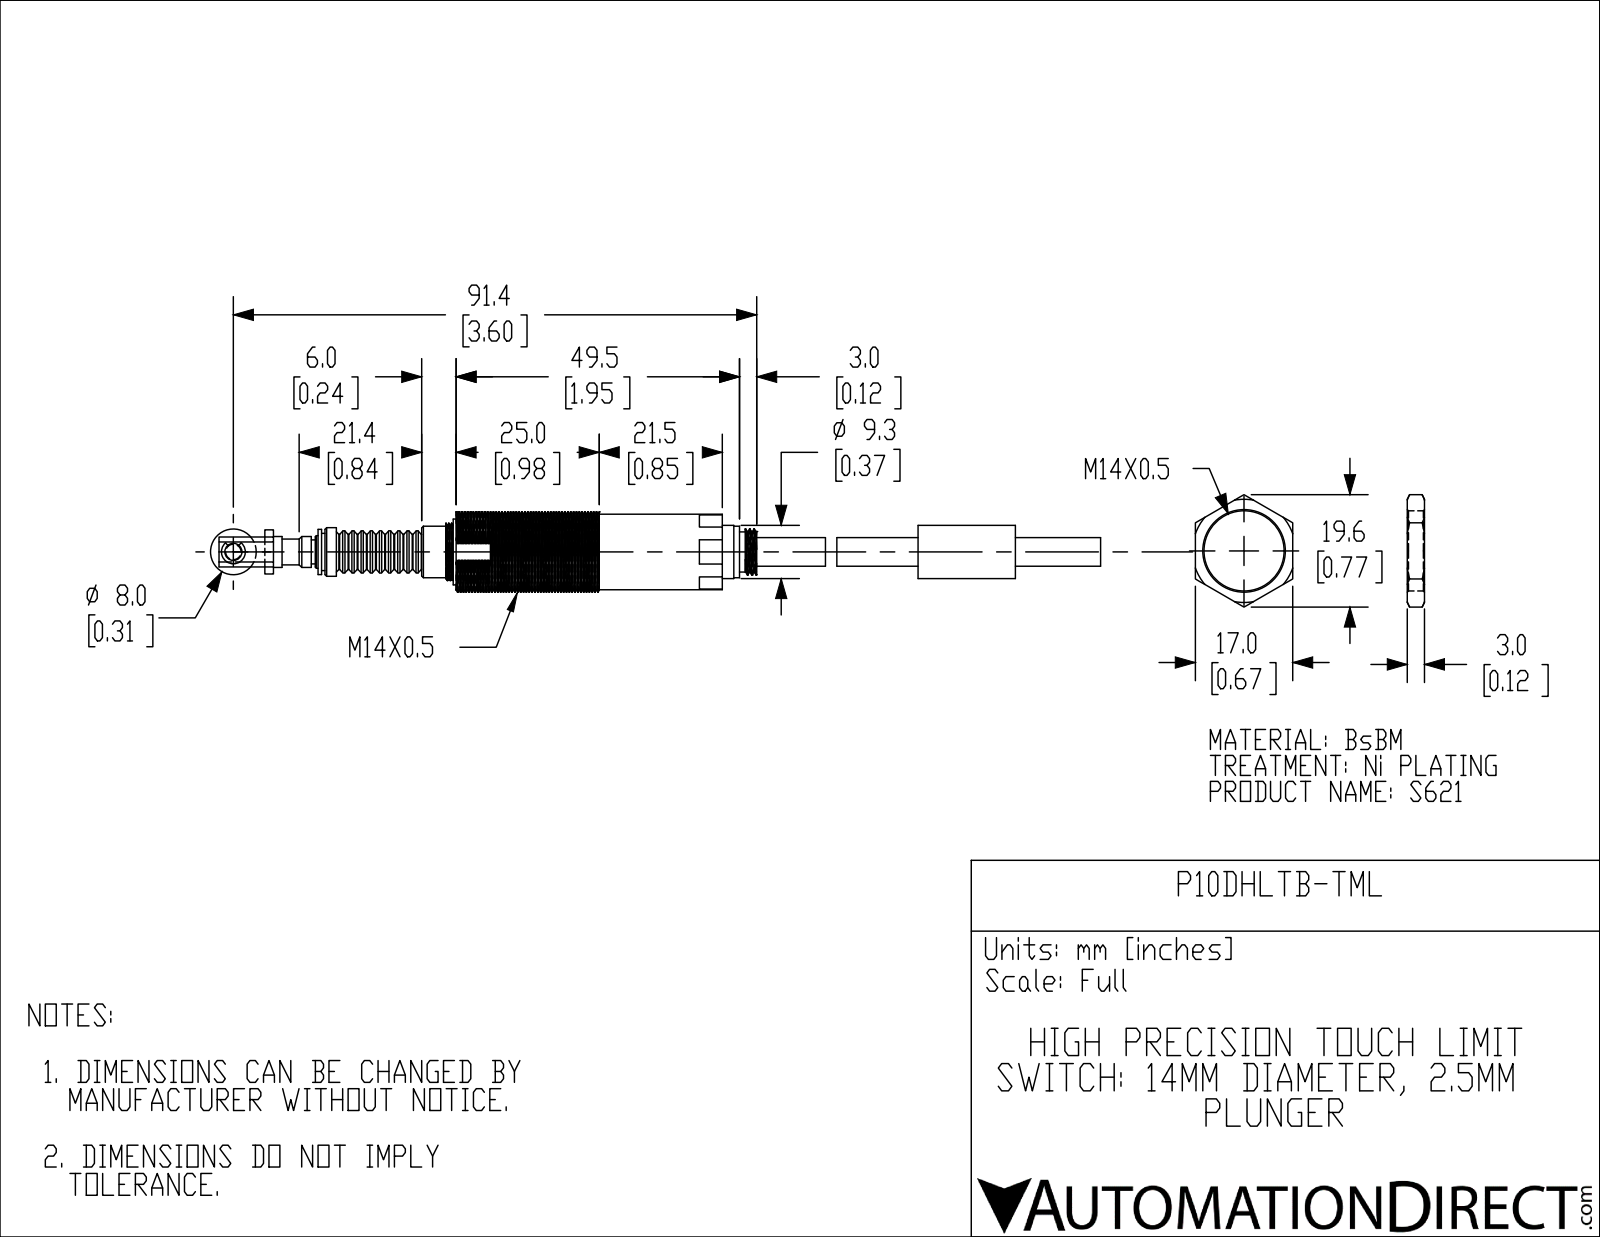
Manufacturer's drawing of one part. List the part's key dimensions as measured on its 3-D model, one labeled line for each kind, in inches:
Part name (STEP PRODUCT): P10DHLTB-TML
STEP written by: SolidWorks 2018 (AUTOMOTIVE_DESIGN)
Units: inches
Bodies: 2 solids, 156 faces (76 planar, 32 cylindrical, 48 other)
Overall size (bounding box): 6.12 × 0.551 × 0.551
Volume: 0.653 in³ · Surface area: 7.95 in²
Round bosses / shafts (diameter × count): ⌀0.315 ×2, ⌀0.551 ×1, ⌀0.52 ×1, ⌀0.453 ×1, ⌀0.394 ×1, ⌀0.366 ×1, ⌀0.354 ×1, ⌀0.335 ×1
Partial cylindrical surfaces — rounded edges, fillets, slot ends (radius × count): R0.082 ×1
Main face-to-face distances: 0.118, 0.197, 0.079, 0.315, 0.12, 0.492, 0.669, 0.199, 0.195, 0.317
